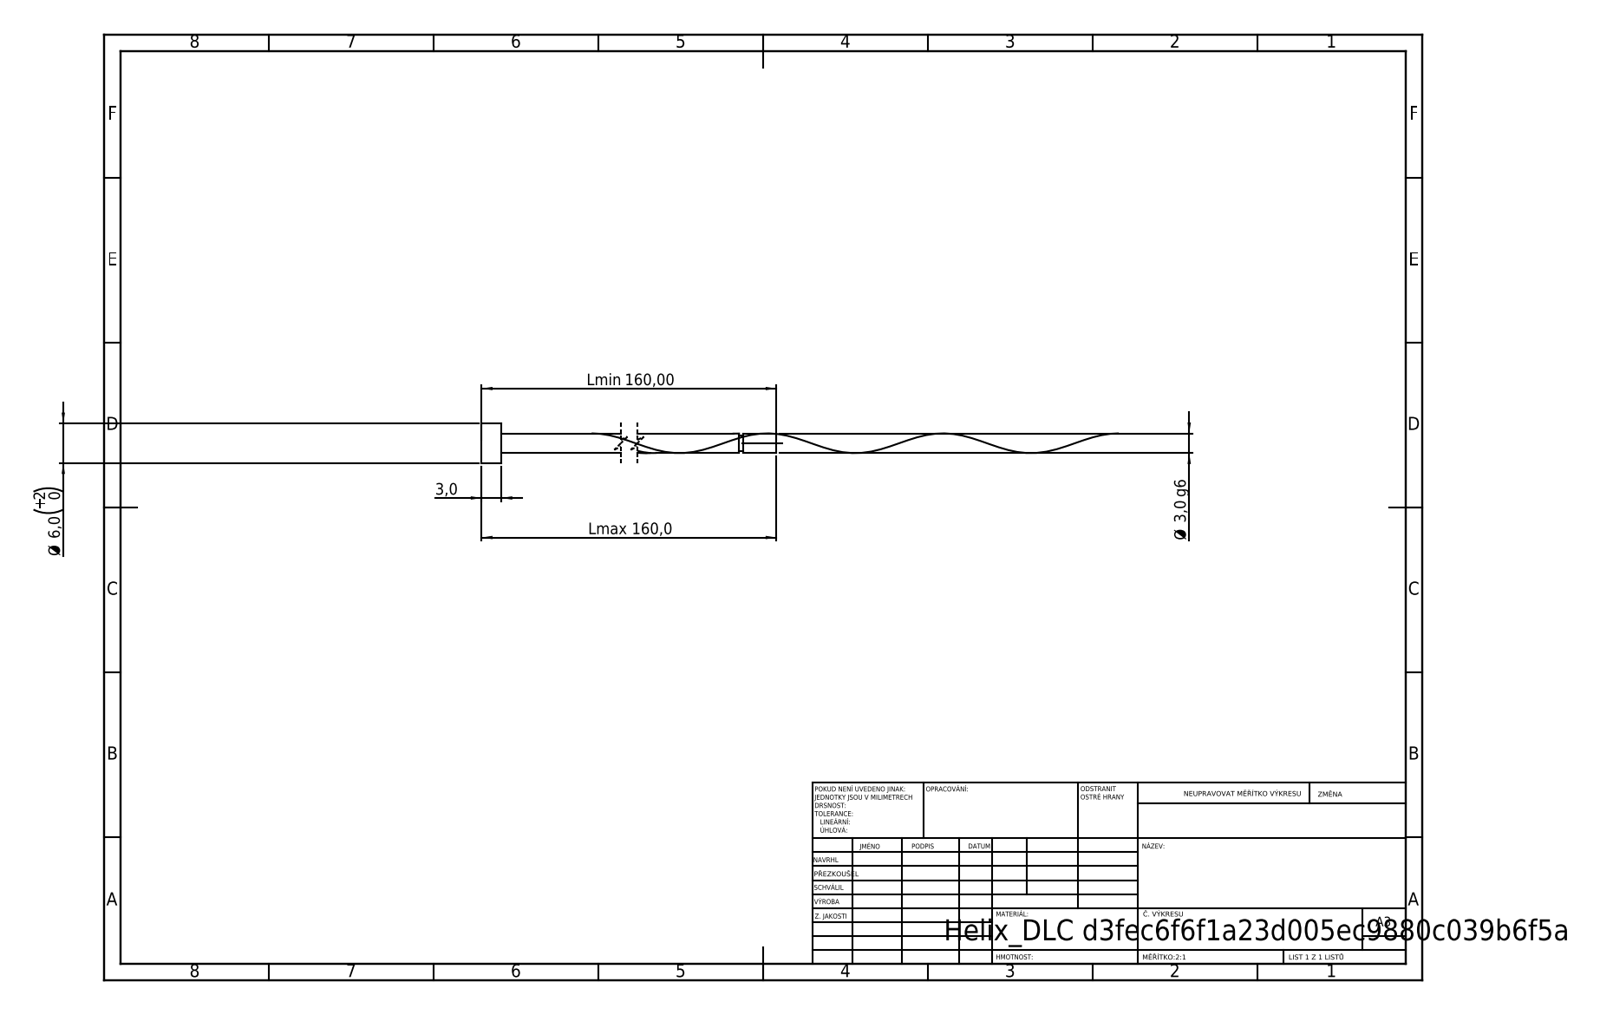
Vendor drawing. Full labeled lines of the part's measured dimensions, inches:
STEP written by: SolidWorks 2019 (CONFIG_CONTROL_DESIGN)
Units: inches
Bodies: 1 solid, 16 faces (6 planar, 9 cylindrical, 1 other)
Overall size (bounding box): 6.299 × 0.236 × 0.236
Volume: 0.087 in³ · Surface area: 3.292 in²
Round bosses / shafts (diameter × count): ⌀0.236 ×1, ⌀0.118 ×1, ⌀0.094 ×1
Main face-to-face distances: 0.118, 6.299, 6.181, 6.099, 5.981, 0.2, 6.075, 5.957, 0.024, 0.224
